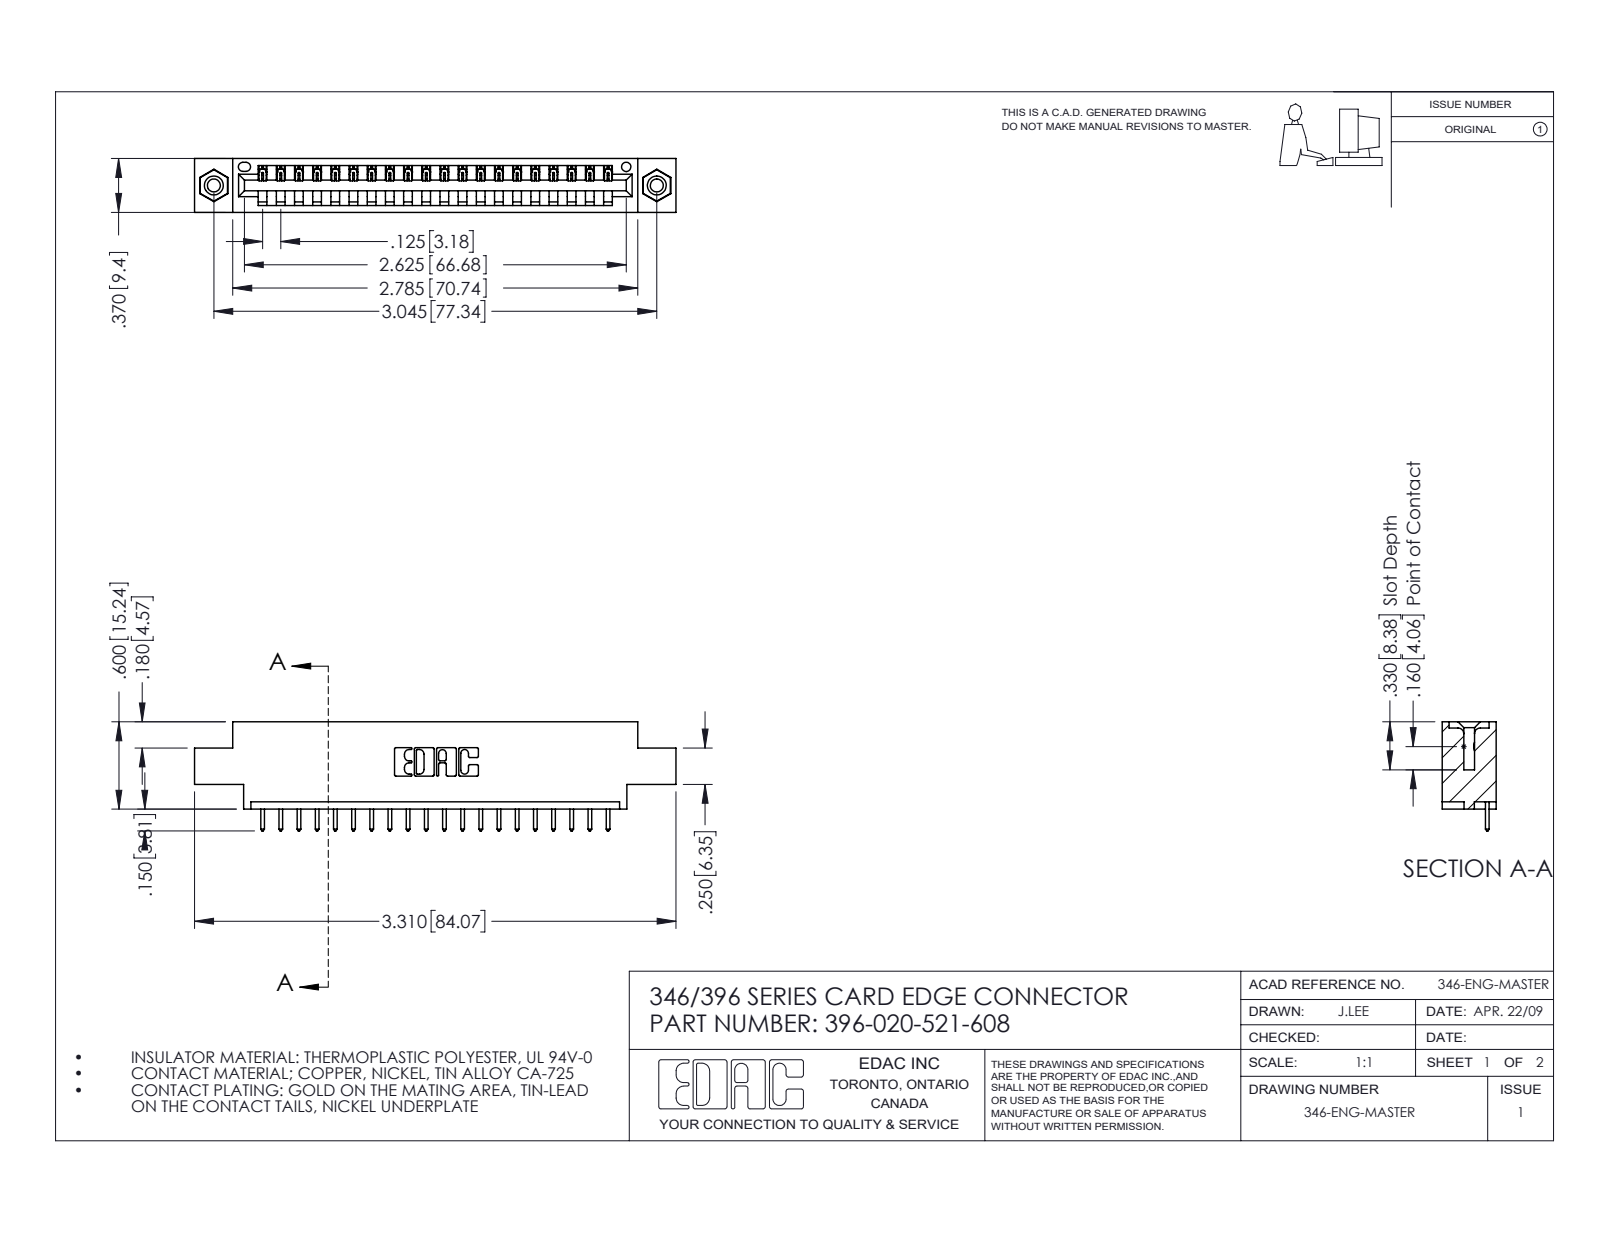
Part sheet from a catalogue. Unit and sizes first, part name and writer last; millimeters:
Units: millimetres
Overall size (bounding box): 84.1 × 19.1 × 9.4
Round holes (diameter × count): ⌀2.3 ×2, ⌀3.2 ×2, ⌀4 ×2, ⌀1.6 ×1
Round bosses / shafts (diameter × count): ⌀3.9 ×2
Partial cylindrical surfaces — rounded edges, fillets, slot ends (radius × count): R0.2 ×40, R0.3 ×40, R0.3 ×22, R0.2 ×6, R0.8 ×6, R0.7 ×3, R0.8 ×2, R1 ×2
Main face-to-face distances: 1.2, 8.2, 9.4, 6.4, 5.6, 1.8, 7.6, 0.6, 3.8, 2.5
Hole centre spacings: 6.2, 72.1, 77.3
Volume: 7 690 mm³ · Surface area: 9 316 mm²
Bodies: 23 solids, 1346 faces (912 planar, 418 cylindrical, 16 other)
Part name (STEP PRODUCT): 346 Part_0.170 Offset - 0.156 Dia-TI; 345-292-001_345-293-121; 345-250-001_345-250-003-102; 396-020-521-608
STEP written by: SolidWorks 2016 (CONFIG_CONTROL_DESIGN)
